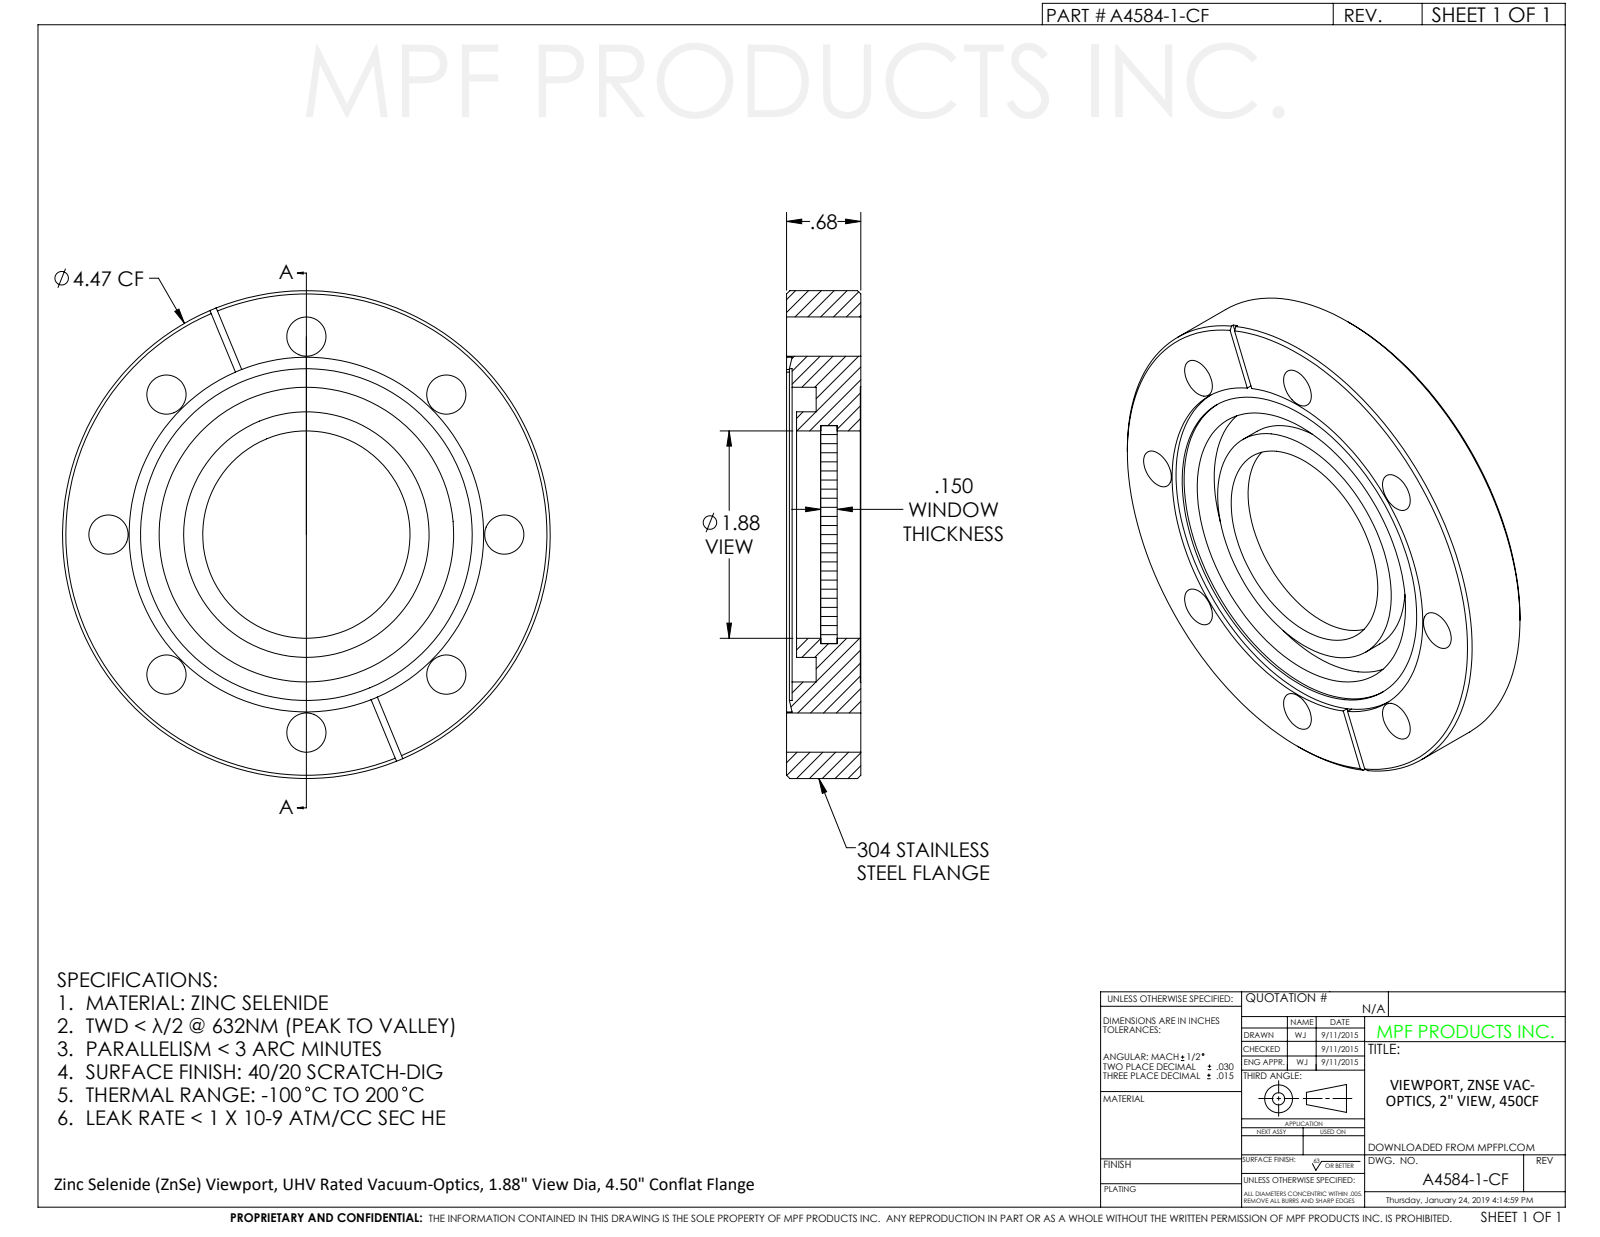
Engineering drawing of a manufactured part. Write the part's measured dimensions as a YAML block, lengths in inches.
part_name: "A4584-1-CF"
step_written_by: "SolidWorks 2011 (CONFIG_CONTROL_DESIGN)"
units: inches
bodies: {solids: 1, faces: 86, planar: 26, cylindrical: 54, other: 6}
overall_size: [4.47, 4.47, 0.68]
volume: 7.609
surface_area: 68.84
round_holes:
  - {diameter: 0.36, count: 8}
  - {diameter: 1.9, count: 1}
  - {diameter: 2.13, count: 1}
  - {diameter: 2.7, count: 1}
  - {diameter: 2.85, count: 1}
  - {diameter: 2.93, count: 1}
  - {diameter: 3.013, count: 1}
  - {diameter: 3.04, count: 1}
  - {diameter: 3.05, count: 1}
  - {diameter: 3.25, count: 1}
round_bosses_or_shafts:
  - {diameter: 4.47, count: 1}
  - {diameter: 3, count: 1}
  - {diameter: 2.87, count: 1}
  - {diameter: 2.813, count: 1}
  - {diameter: 2.77, count: 1}
  - {diameter: 2.75, count: 1}
  - {diameter: 2.25, count: 1}
  - {diameter: 2, count: 1}
face_to_face_distances: [0.68, 0.676, 0.213, 0.363, 0.375, 0.15, 0.367, 0.313, 0.217, 0.463]
hole_center_spacings: [1.814, 2.565, 3.352, 1.388, 1.389, 3.628]
